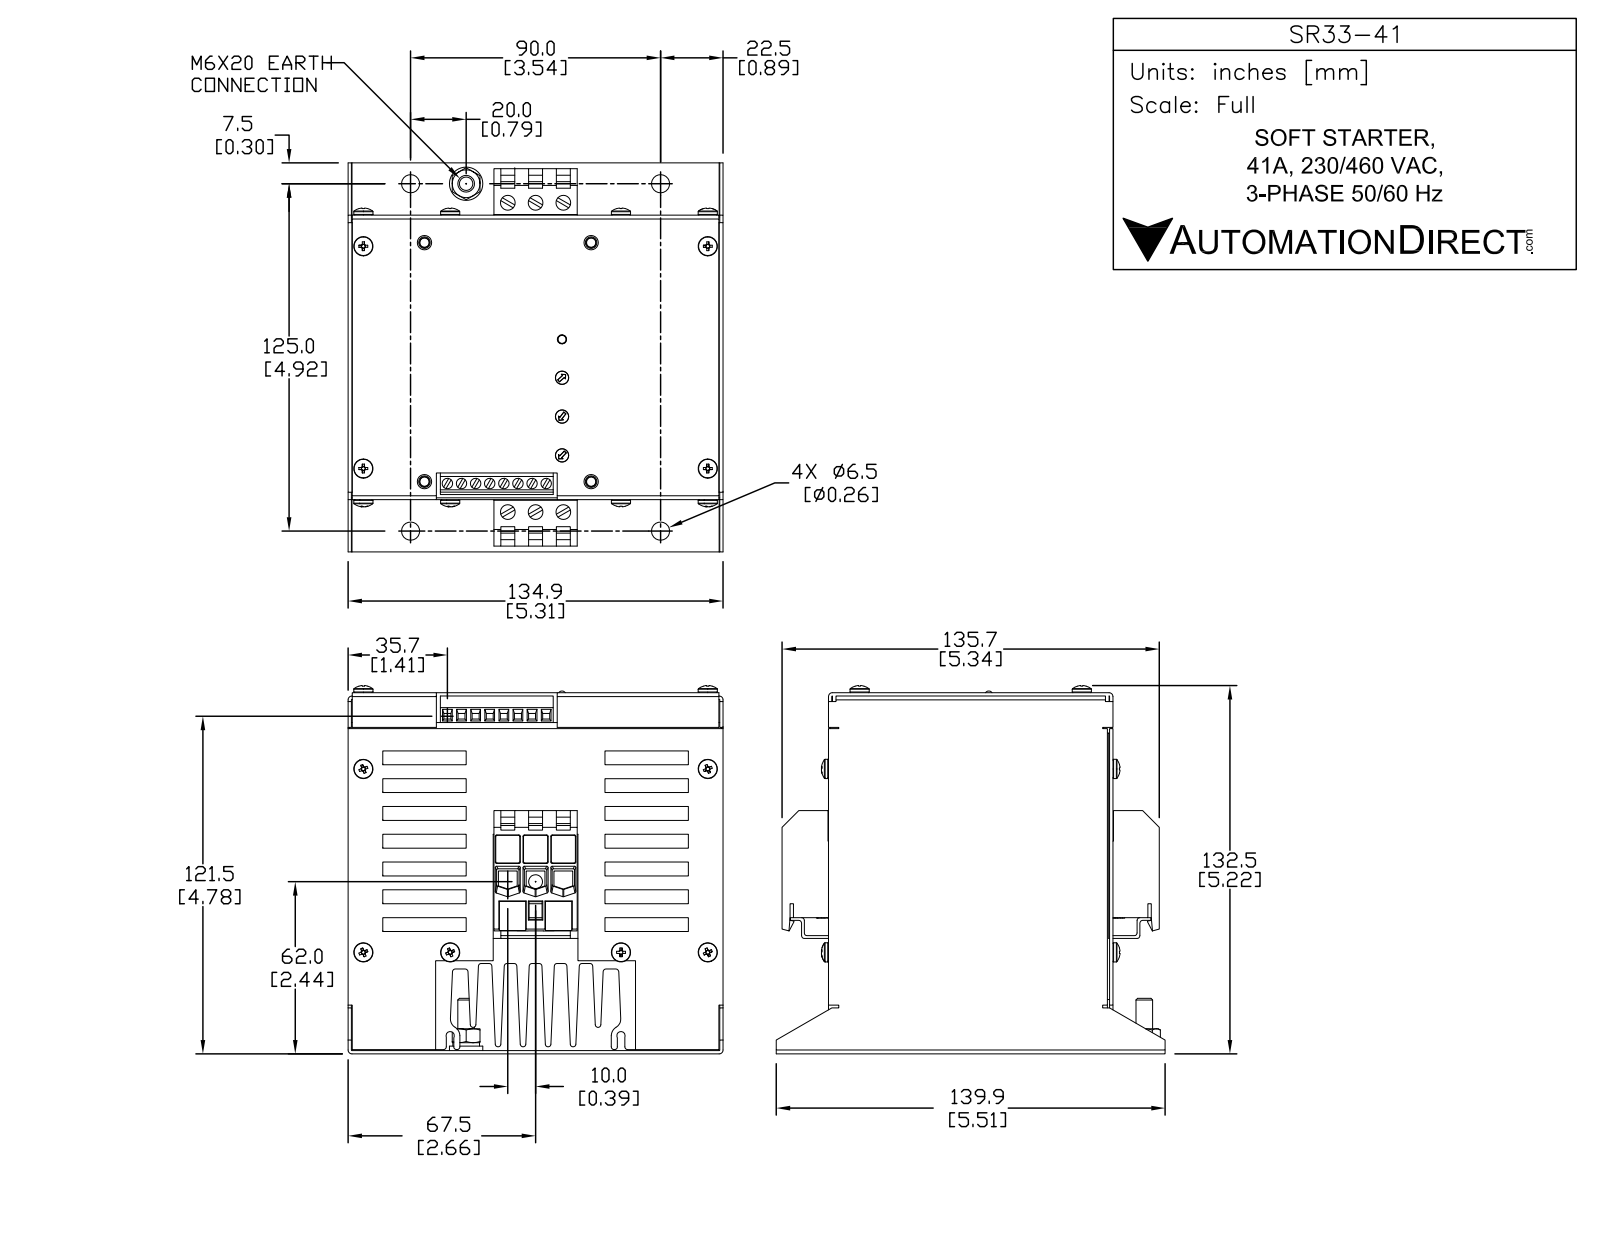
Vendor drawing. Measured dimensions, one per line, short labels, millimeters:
name: SR33-41
written by: SolidWorks 2013 (AUTOMOTIVE_DESIGN)
unit: mm
bodies: 1 solid, 980 faces (712 planar, 170 cylindrical, 98 other)
size: 139.9 × 134.9 × 132.9
volume: 1 475 000 mm³; area: 260 135 mm²
holes: 8× ⌀3.82, 6× ⌀5, 4× ⌀6.5
bosses: 10× ⌀6.9, 1× ⌀12, 1× ⌀6
rounds: 30× R1, 14× R0.44, 5× R3, 4× R2, 3× R0.57, 2× R0.5, 2× R0.52, 2× R0.52
face distances: 5, 10, 15, 20, 30, 25, 35, 40, 45, 50
hole spacings: 10, 5, 20, 15, 35.55, 45.43, 55.35, 113.02
